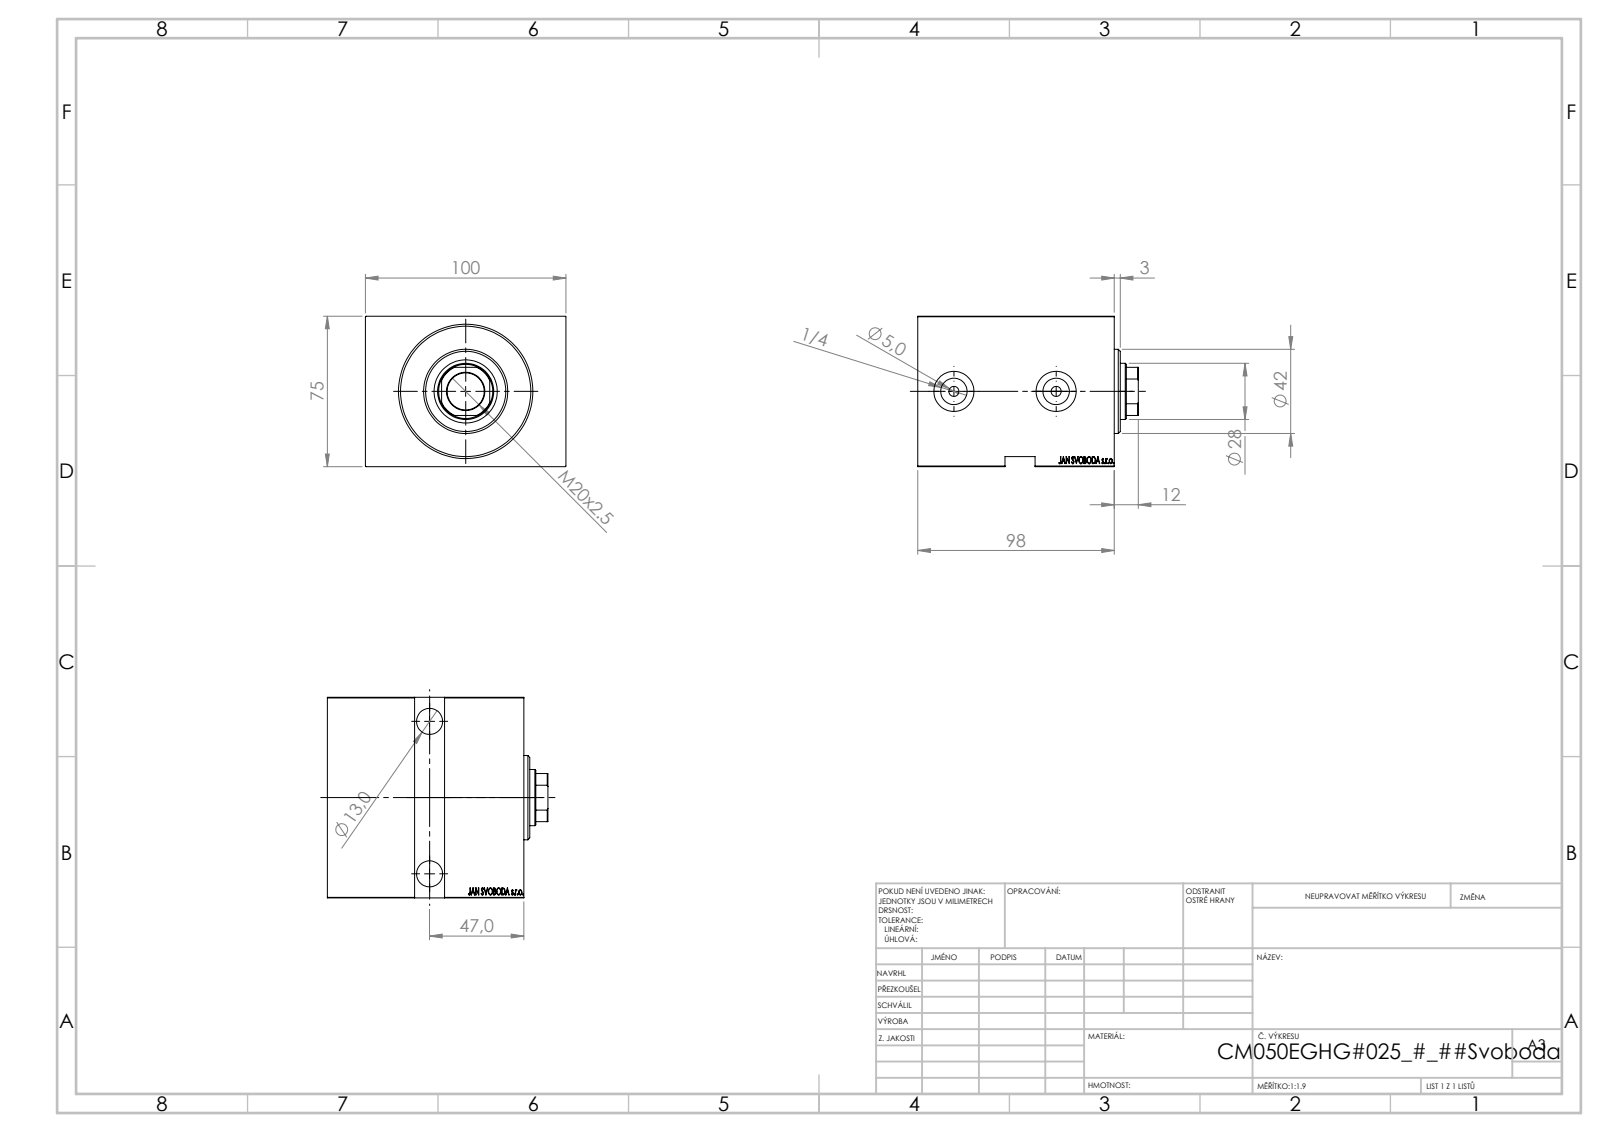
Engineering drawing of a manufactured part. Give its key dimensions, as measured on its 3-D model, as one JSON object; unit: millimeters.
{"part_name": "V450CM_E_VCP; V450CM_VC_B; V450CM_E_Body", "step_written_by": "SolidWorks 2019 (CONFIG_CONTROL_DESIGN)", "units": "millimeters", "bodies": {"solids": 3, "faces": 846, "planar": 408, "cylindrical": 44, "other": 394}, "overall_size": [110, 100, 75], "volume_mm3": 706272, "surface_area_mm2": 103753, "round_holes": [[5, 2], [13, 2], [13.16, 2], [19, 2], [20, 2], [18.5, 1], [28, 1], [31.5, 1], [50, 1], [65, 1]], "round_bosses_or_shafts": [[52, 1], [42, 1]], "partial_cylinders_radius": [[13.5, 1]], "face_to_face_distances": [75, 100, 98, 14, 84, 5, 93, 79, 38, 33], "hole_center_spacings": [51, 76]}
